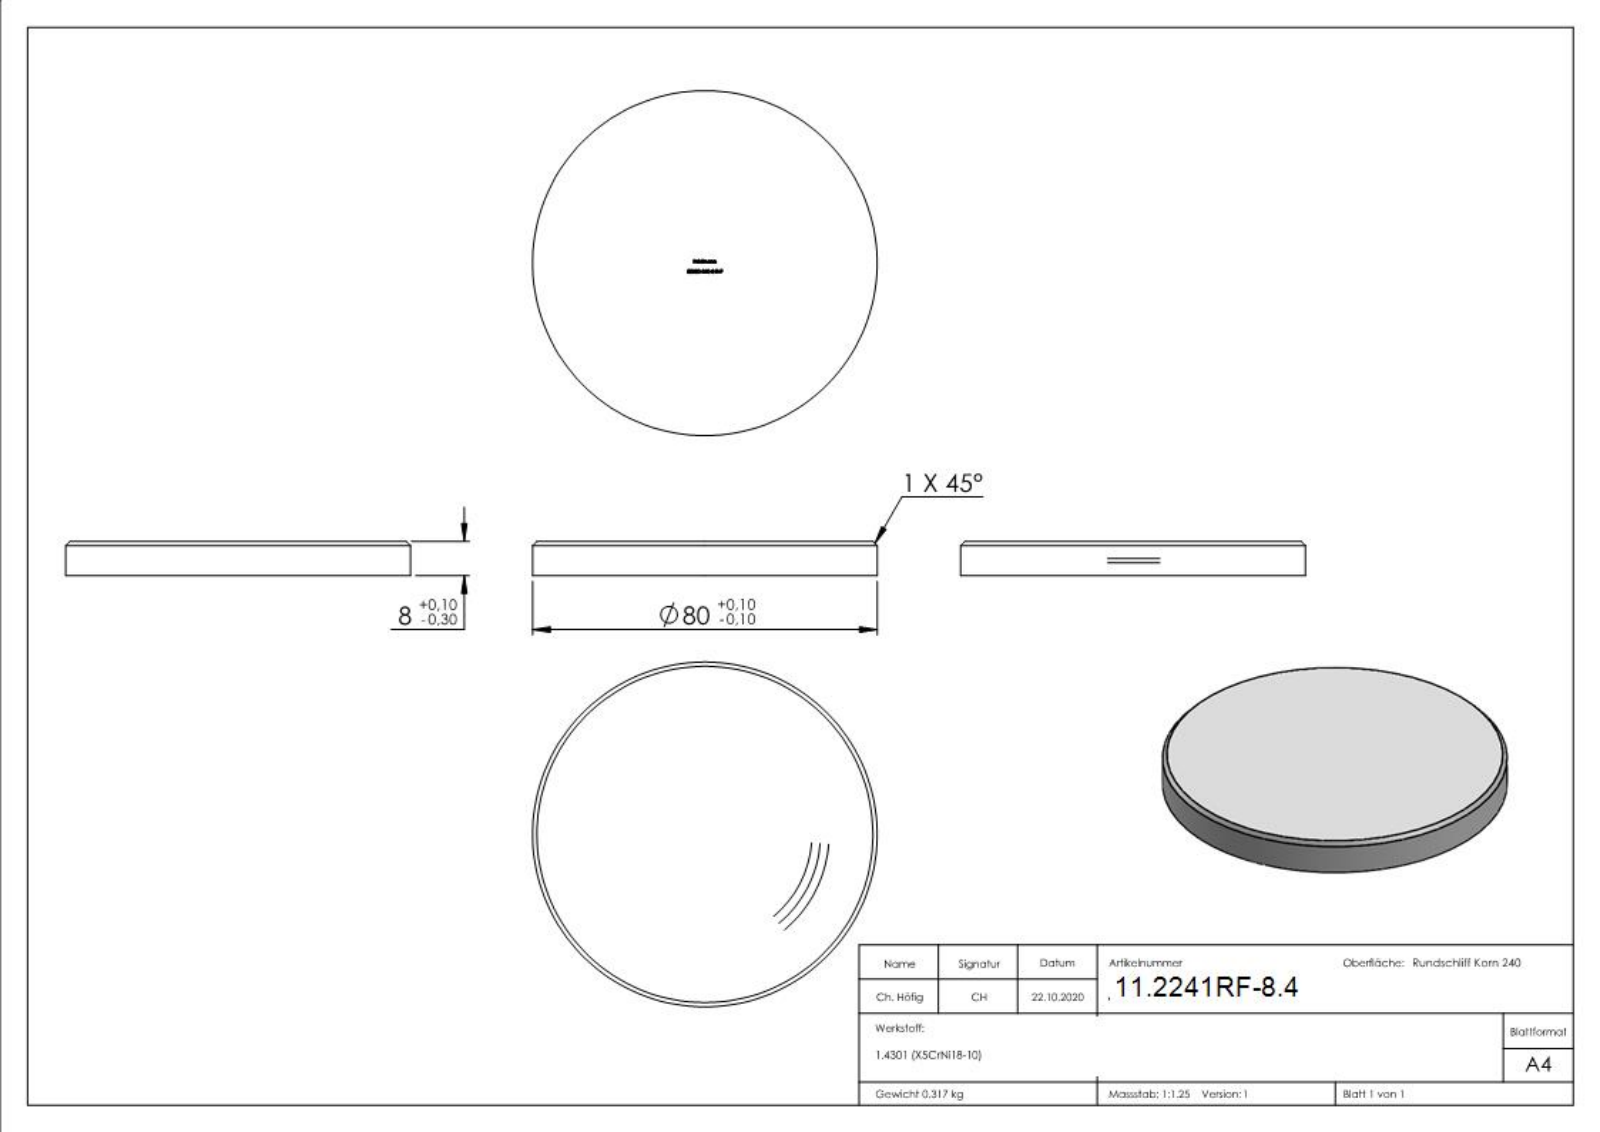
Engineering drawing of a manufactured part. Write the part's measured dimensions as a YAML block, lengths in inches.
part_name: "53080-240-8-R-F"
step_written_by: "SolidWorks 2018 (CONFIG_CONTROL_DESIGN)"
units: inches
bodies: {solids: 1, faces: 302, planar: 156, cylindrical: 2, other: 144}
overall_size: [3.15, 3.15, 0.315]
volume: 2.446
surface_area: 18.48
round_bosses_or_shafts:
  - {diameter: 3.15, count: 1}
face_to_face_distances: [0.315, 0.311, 0.048, 0.157, 0.068, 0.088, 0.092, 0.091, 0.07, 0.041]
